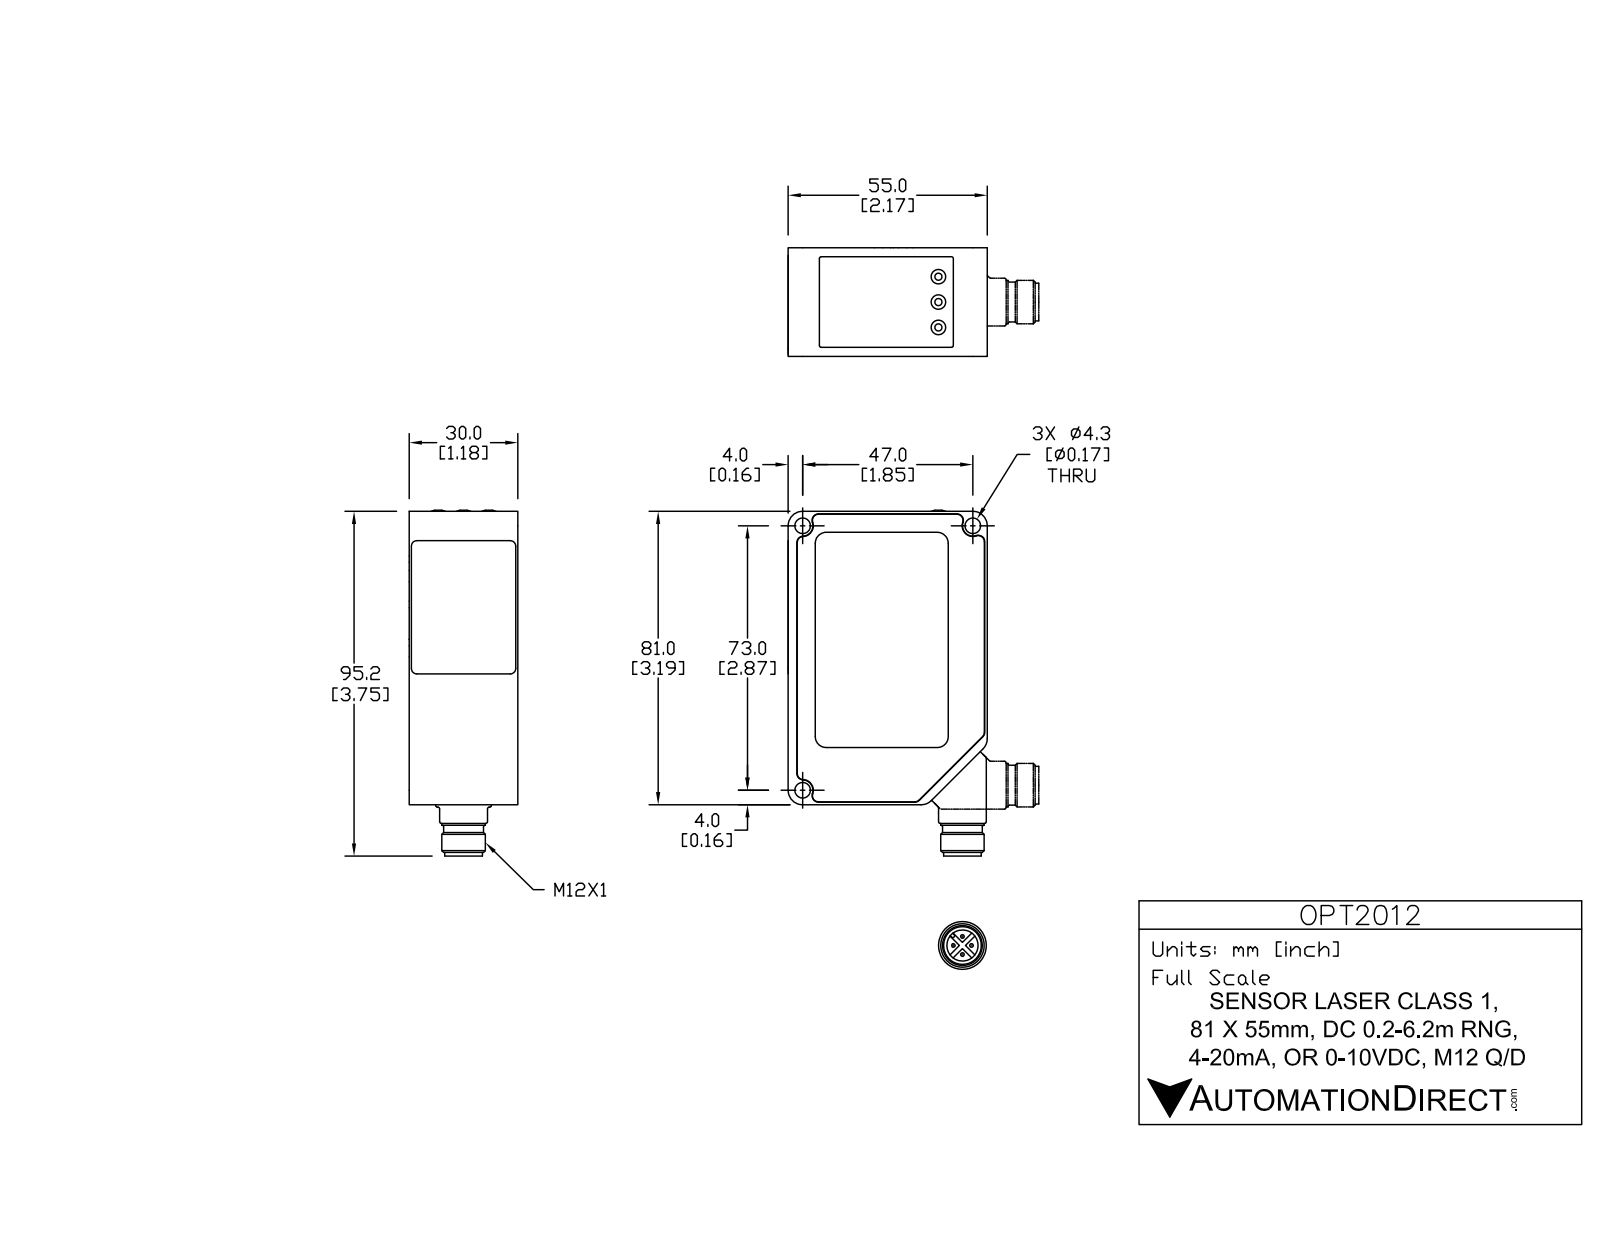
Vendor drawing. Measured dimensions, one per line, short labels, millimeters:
name: OPT2012
written by: SolidWorks 2013 (AUTOMOTIVE_DESIGN)
unit: mm
bodies: 17 solids, 305 faces (160 planar, 137 cylindrical, 8 other)
size: 95.83 × 55 × 30
volume: 122 805 mm³; area: 29 589 mm²
holes: 3× ⌀4.25, 1× ⌀5, 1× ⌀8.45
bosses: 4× ⌀1, 3× ⌀4.5, 1× ⌀18, 1× ⌀13.5, 1× ⌀12, 1× ⌀11, 1× ⌀10.3
rounds: 18× R2, 8× R1.25, 6× R2.1, 4× R0.5, 4× R1, 4× R1.5, 3× R1.9, 2× R0.75
face distances: 30, 55, 29.8, 3, 0.8, 81, 78, 54.8, 80.2, 2.2
hole spacings: 47, 73, 86.82
